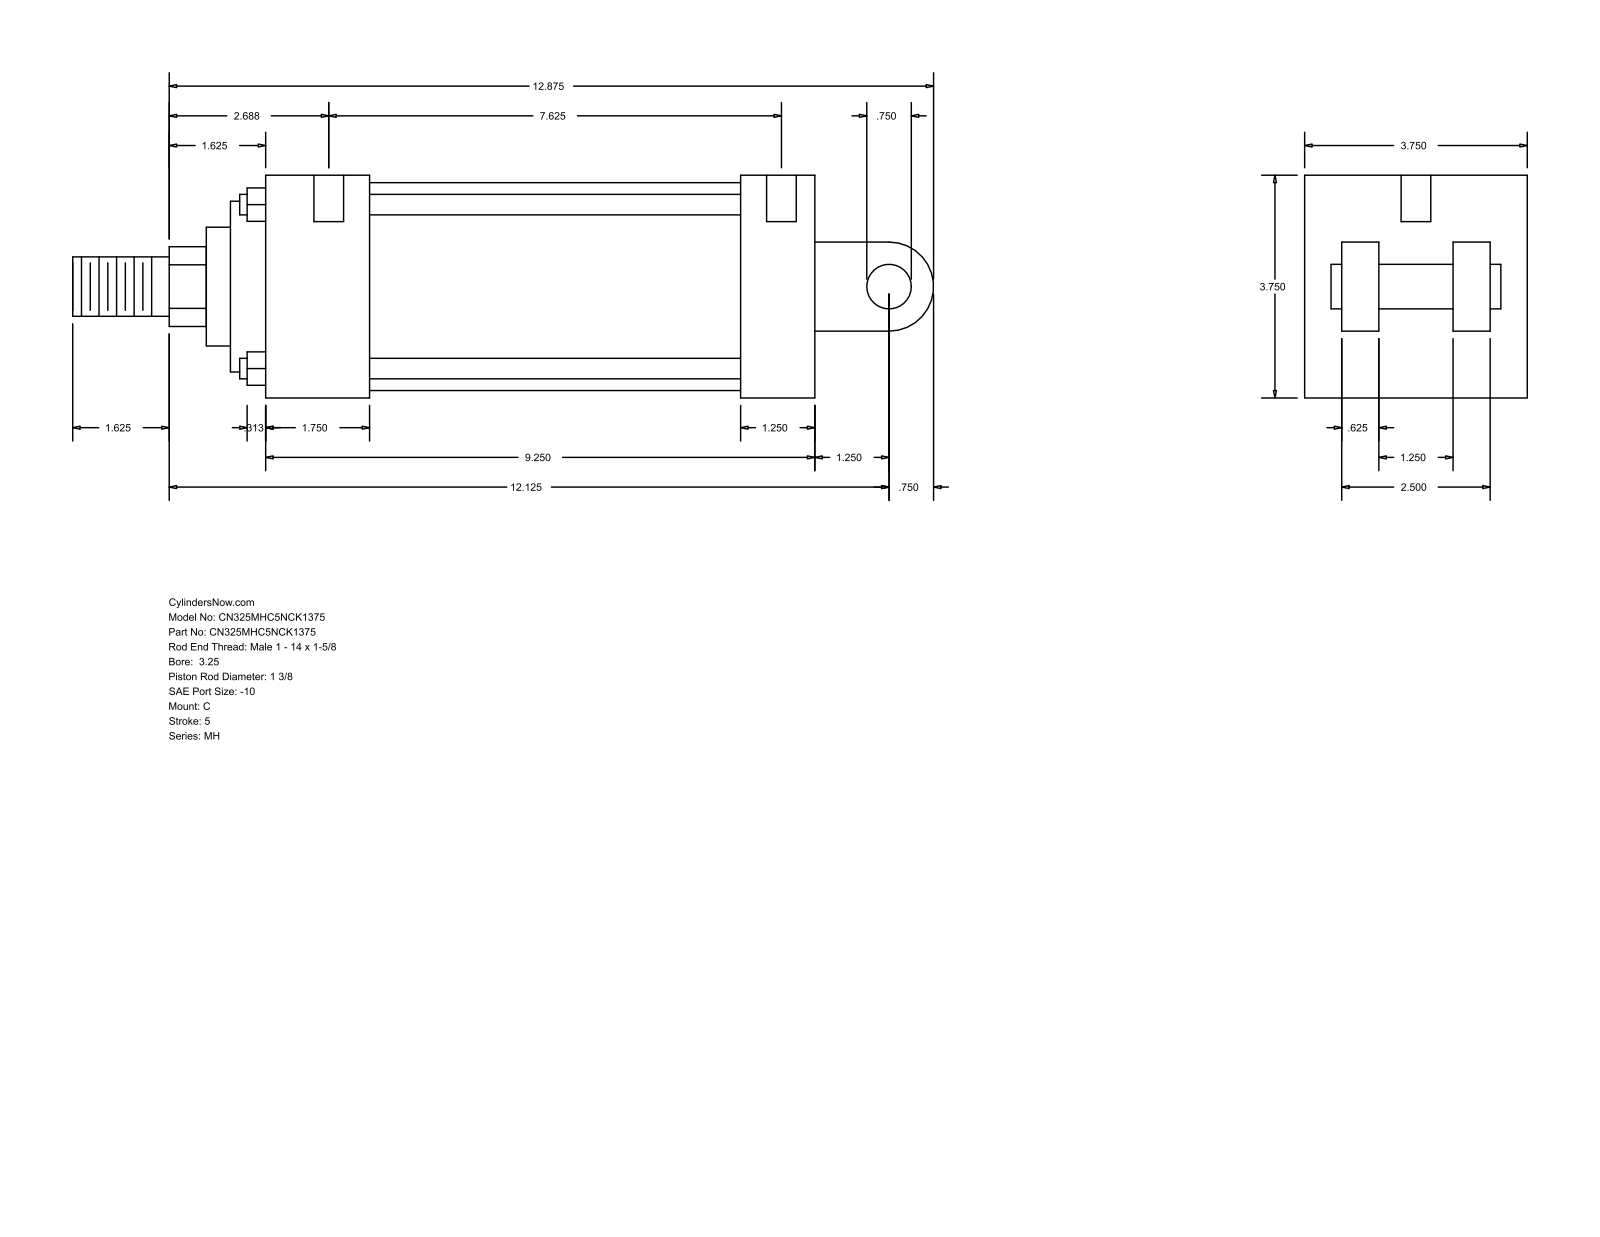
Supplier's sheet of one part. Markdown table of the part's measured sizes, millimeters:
| quantity | value |
| --- | --- |
| part name | MH_C__0325_1.375 |
| STEP written by | GSSL Pune (CONFIG_CONTROL_DESIGN) |
| units | millimeters |
| bodies | 0 solids, 101 faces (71 planar, 30 cylindrical, 0 other) |
| overall size | 368.3 × 95.25 × 95.25 |
| round holes (diameter × count) | 5.56 × 4, 12.7 × 2 |
| round bosses / shafts (diameter × count) | 8.76 × 4, 88.9 × 1, 73.03 × 1, 50.8 × 1, 34.92 × 1, 25.4 × 1, 19.05 × 1 |
| partial cylindrical surfaces (radius × count) | 17.06 × 1, 19.05 × 1 |
| main face-to-face distances | 95.24, 15.87, 63.5, 234.96, 31.76, 79.37, 31.74, 47.63, 44.45, 203.2 |
| hole center spacings | 200.03, 1.59, 4.76, 193.68, 195.27, 198.44 |
